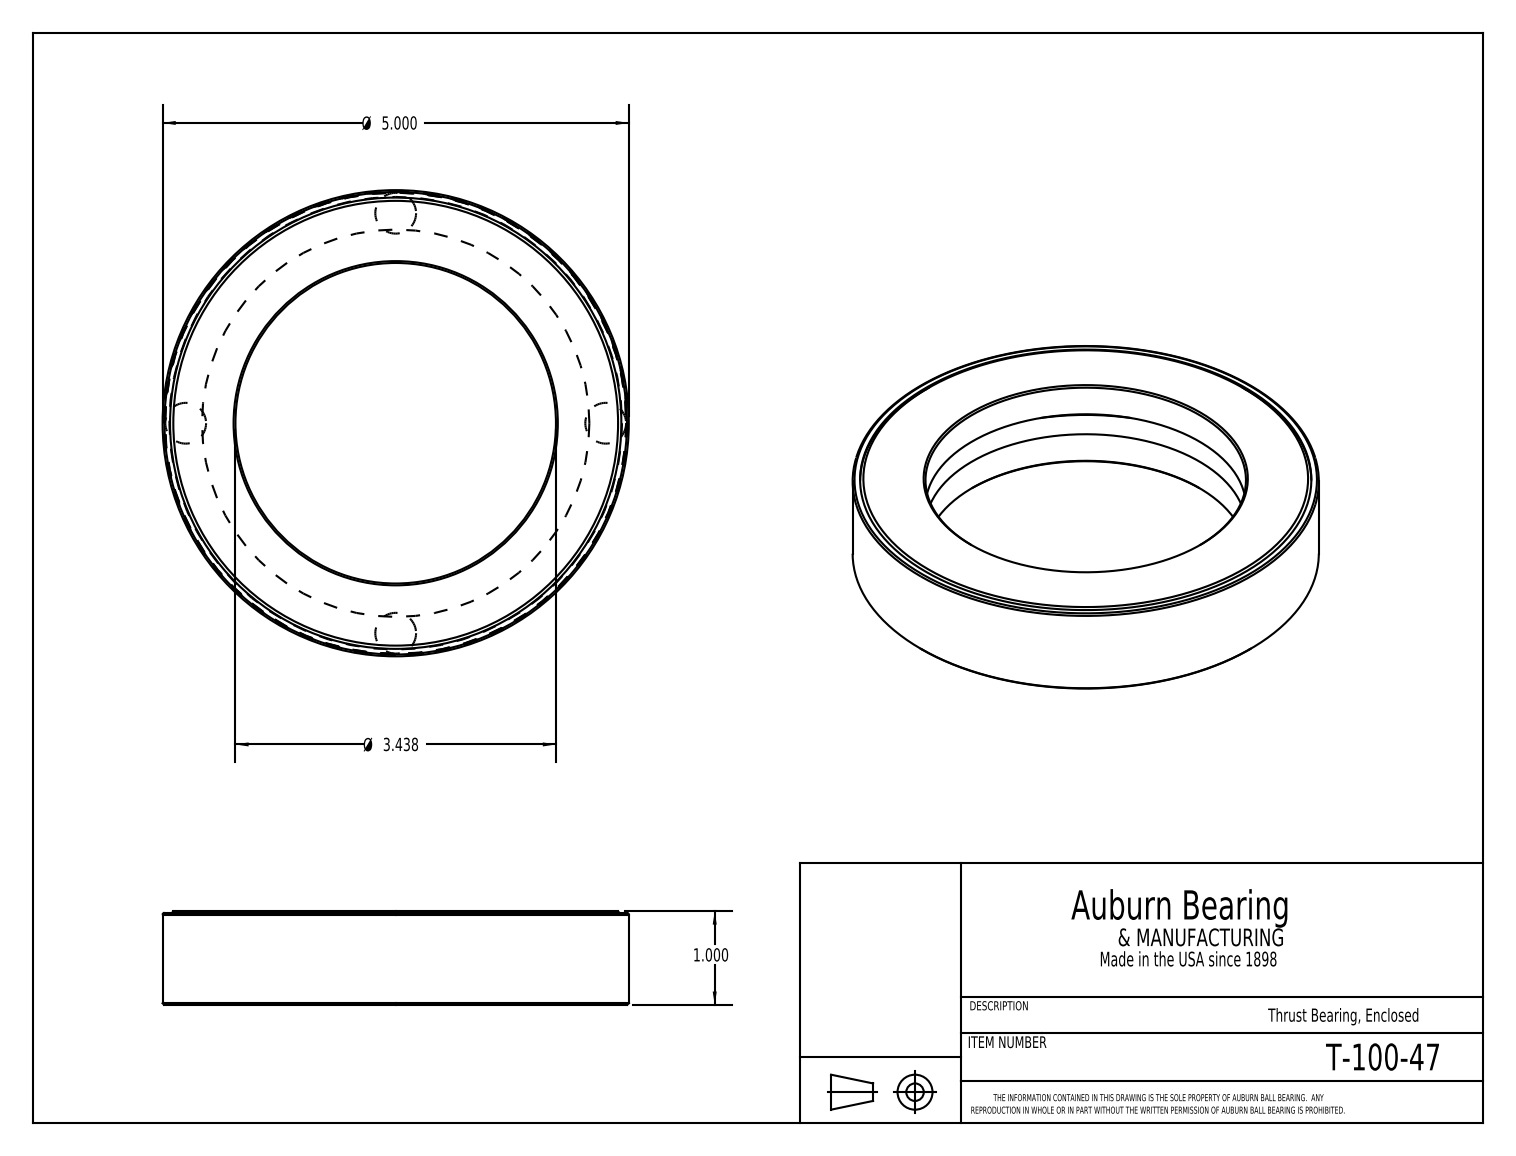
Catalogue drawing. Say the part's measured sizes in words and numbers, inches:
The part is named "T-100-47". Its 3-D file was written by "SolidWorks 2016 (CONFIG_CONTROL_DESIGN)". It is 6 solids with 28 faces: 9 planar, 7 cylindrical and 12 other. Overall it measures 5 by 5 by 1 inches. Its volume is 7.195 cubic inches and its surface area 83.94 square inches. Round holes: 1 of diameter 3.437, 1 of diameter 4.84, 1 of diameter 4.96. Round bosses or shafts: 1 of diameter 5, 1 of diameter 4.946. The main face-to-face distances are 0.369, 0.631, 1, 0.262, 0.965, 0.985, 0.596, 0.616, 0.334, 0.354.
